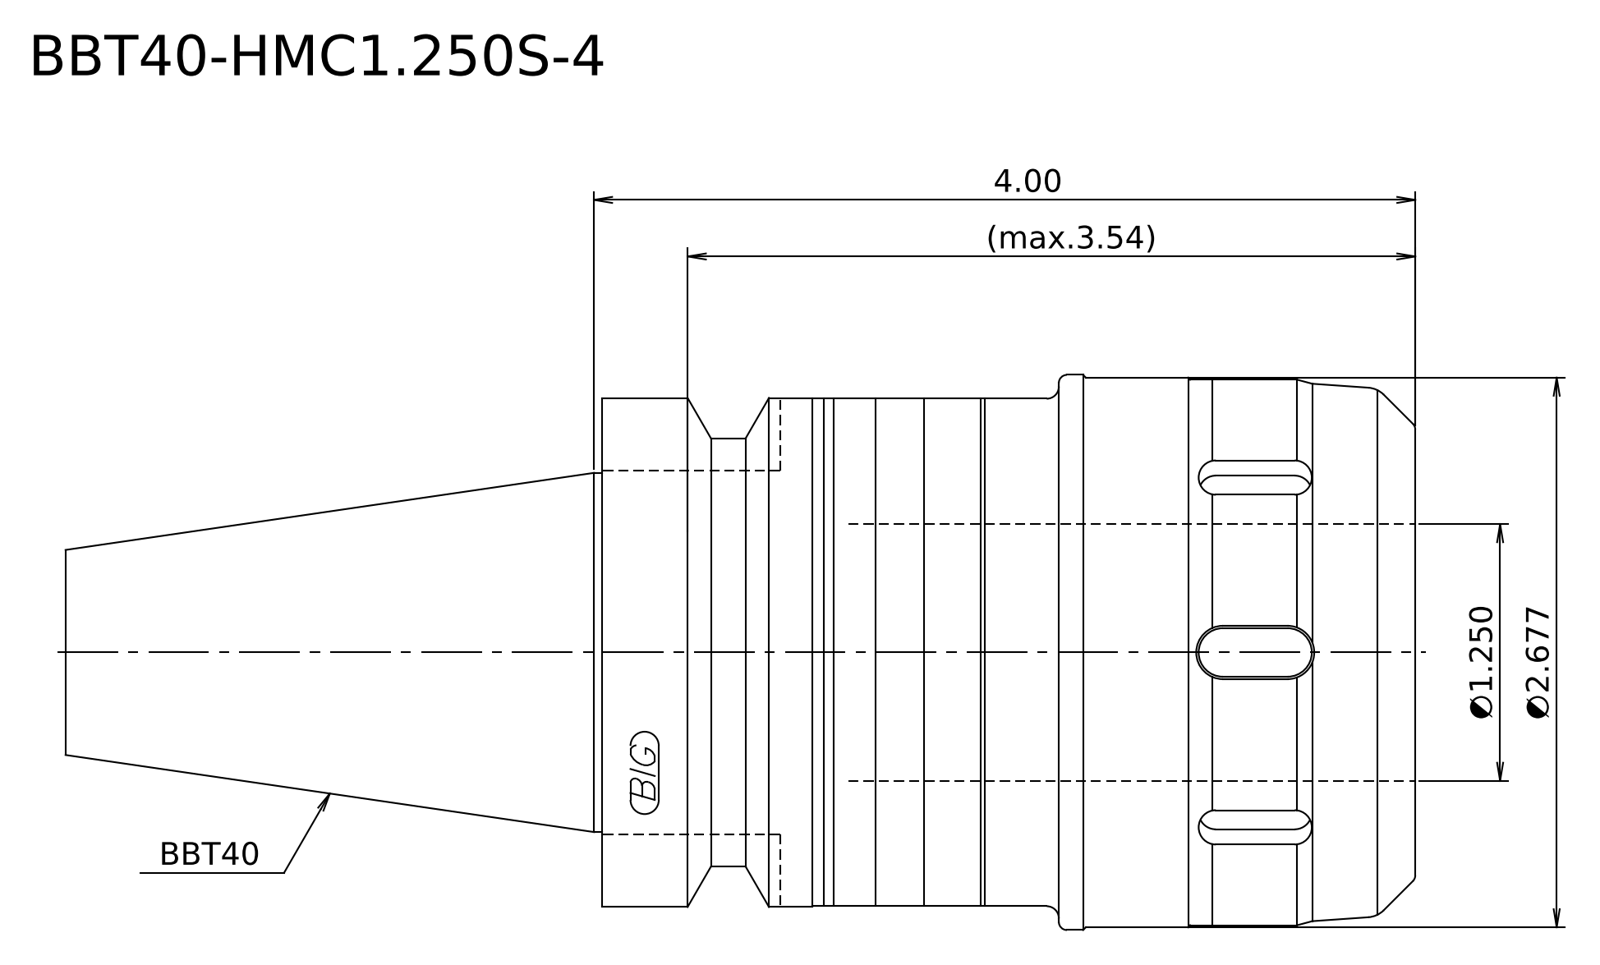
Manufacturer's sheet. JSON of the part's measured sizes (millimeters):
{"step_written_by": "Kubotek KeyCreator 2011 V10.0.2 (22737) (automotive_design)", "units": "millimeters", "bodies": {"solids": 1, "faces": 22, "planar": 5, "cylindrical": 8, "other": 9}, "overall_size": [167, 68.7, 68.7], "volume_mm3": 389149, "surface_area_mm2": 34054, "round_bosses_or_shafts": [[68.7, 1], [68, 1], [67.5, 1], [63, 1], [62.8, 1], [53, 1], [44.45, 1]], "face_to_face_distances": [100.6, 167, 66.4, 44.1, 56.5, 122.9, 74.6, 30.5, 26, 92.4]}
